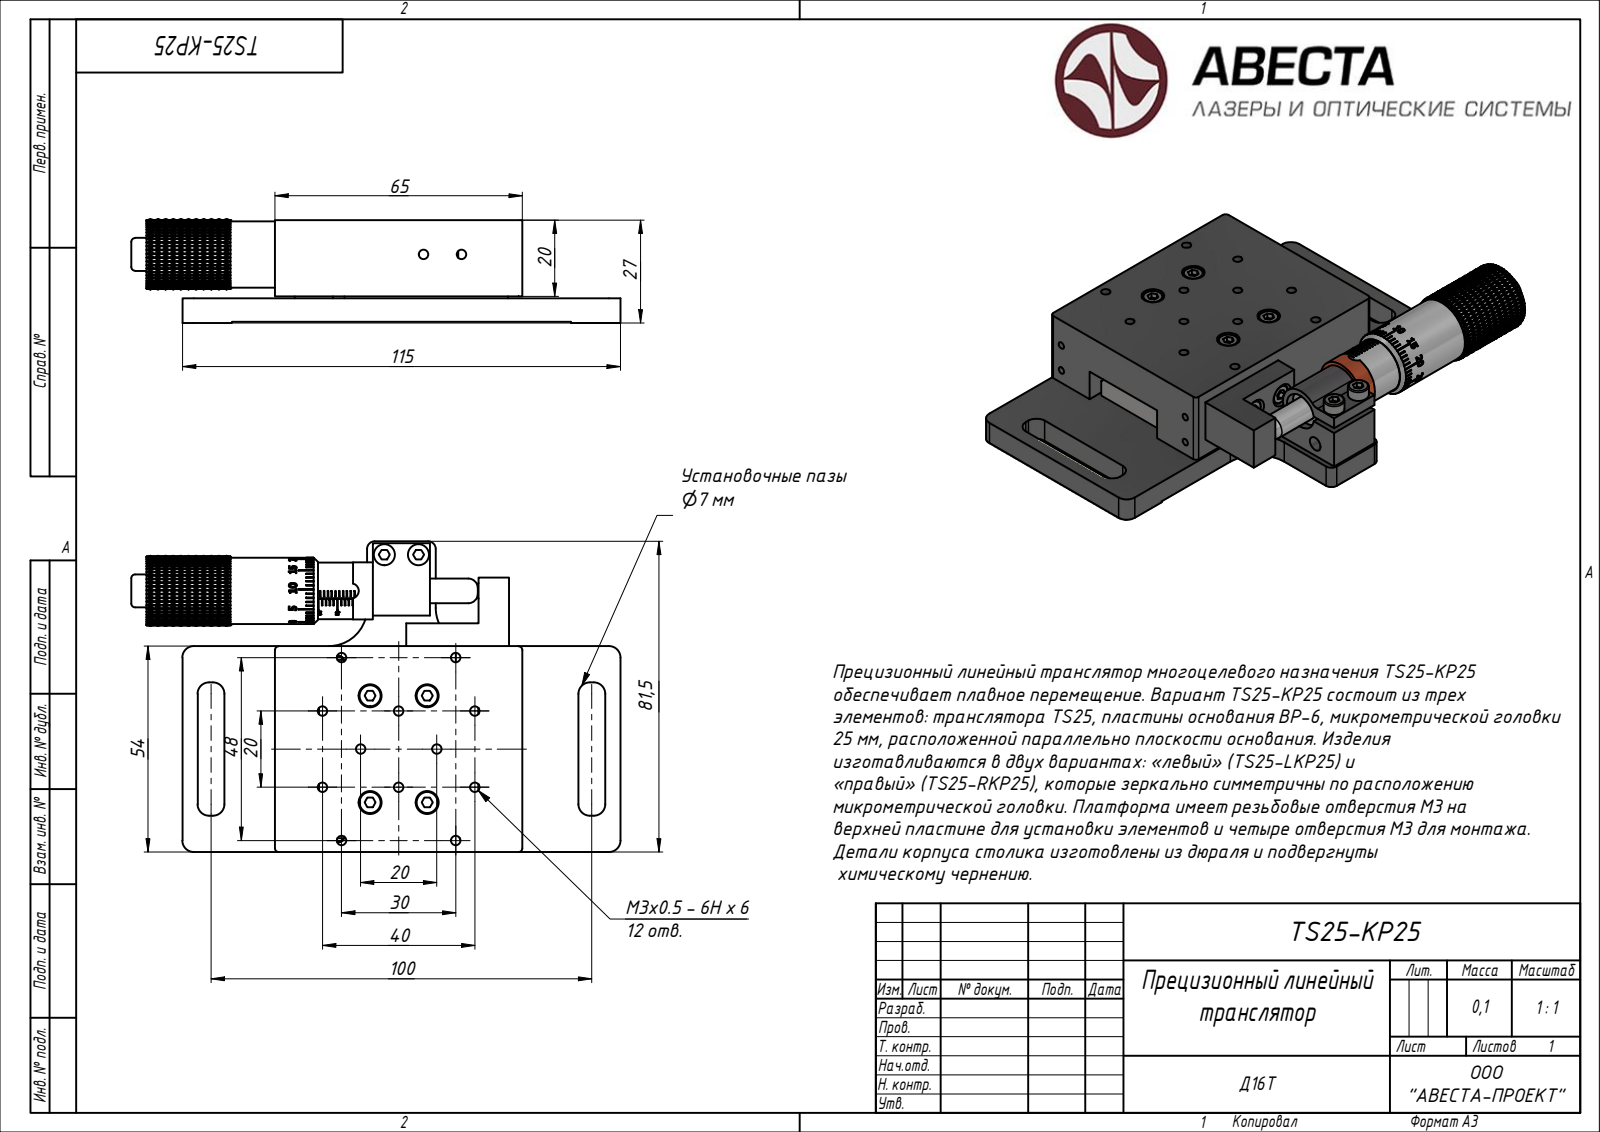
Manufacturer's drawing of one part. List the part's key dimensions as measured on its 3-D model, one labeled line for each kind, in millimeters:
Part name (STEP PRODUCT): Block 01
STEP written by: ST-DEVELOPER v15 (AUTOMOTIVE_DESIGN)
Units: millimetres
Bodies: 12 solids, 653 faces (0 planar, 0 cylindrical, 653 other)
Overall size (bounding box): 133.2 × 81.5 × 27
